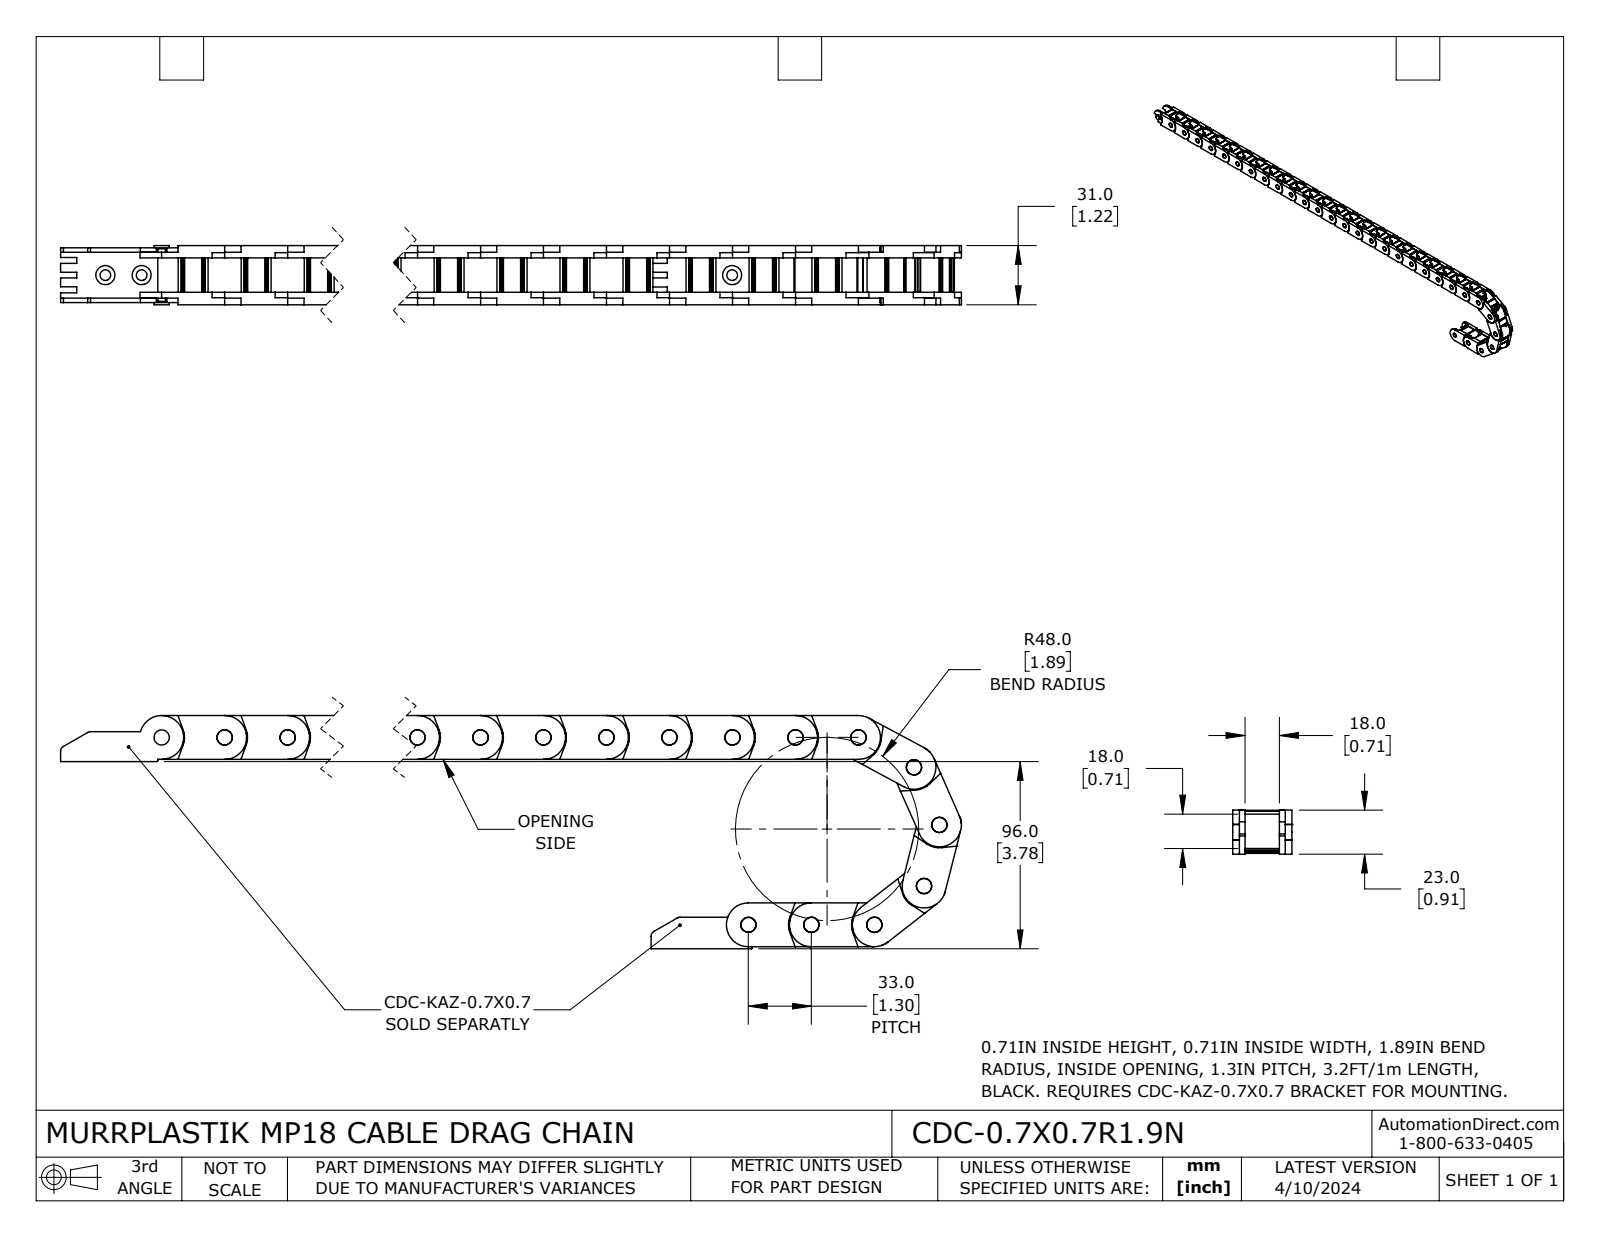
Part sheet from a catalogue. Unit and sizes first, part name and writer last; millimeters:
Units: millimetres
Overall size (bounding box): 857.22 × 121.09 × 31
Round holes (diameter × count): ⌀8 ×30
Round bosses / shafts (diameter × count): ⌀8 ×1
Partial cylindrical surfaces — rounded edges, fillets, slot ends (radius × count): R0.5 ×120, R1.5 ×120, R0.2 ×60, R0.3 ×60, R11.5 ×31, R11.95 ×31, R5 ×30, R5.45 ×30
Main face-to-face distances: 6.5, 24.5, 31, 18, 3.5, 27.5, 3, 21, 3.7, 27.3
Hole centre spacings: 33, 66, 99, 132, 165, 198, 231, 264
Volume: 298 198 mm³ · Surface area: 212 463 mm²
Bodies: 30 solids, 2790 faces (1530 planar, 1260 cylindrical, 0 other)
Part name (STEP PRODUCT): CDC-0.7X0.7R1.9N
STEP written by: SolidWorks 2023 (CONFIG_CONTROL_DESIGN)
